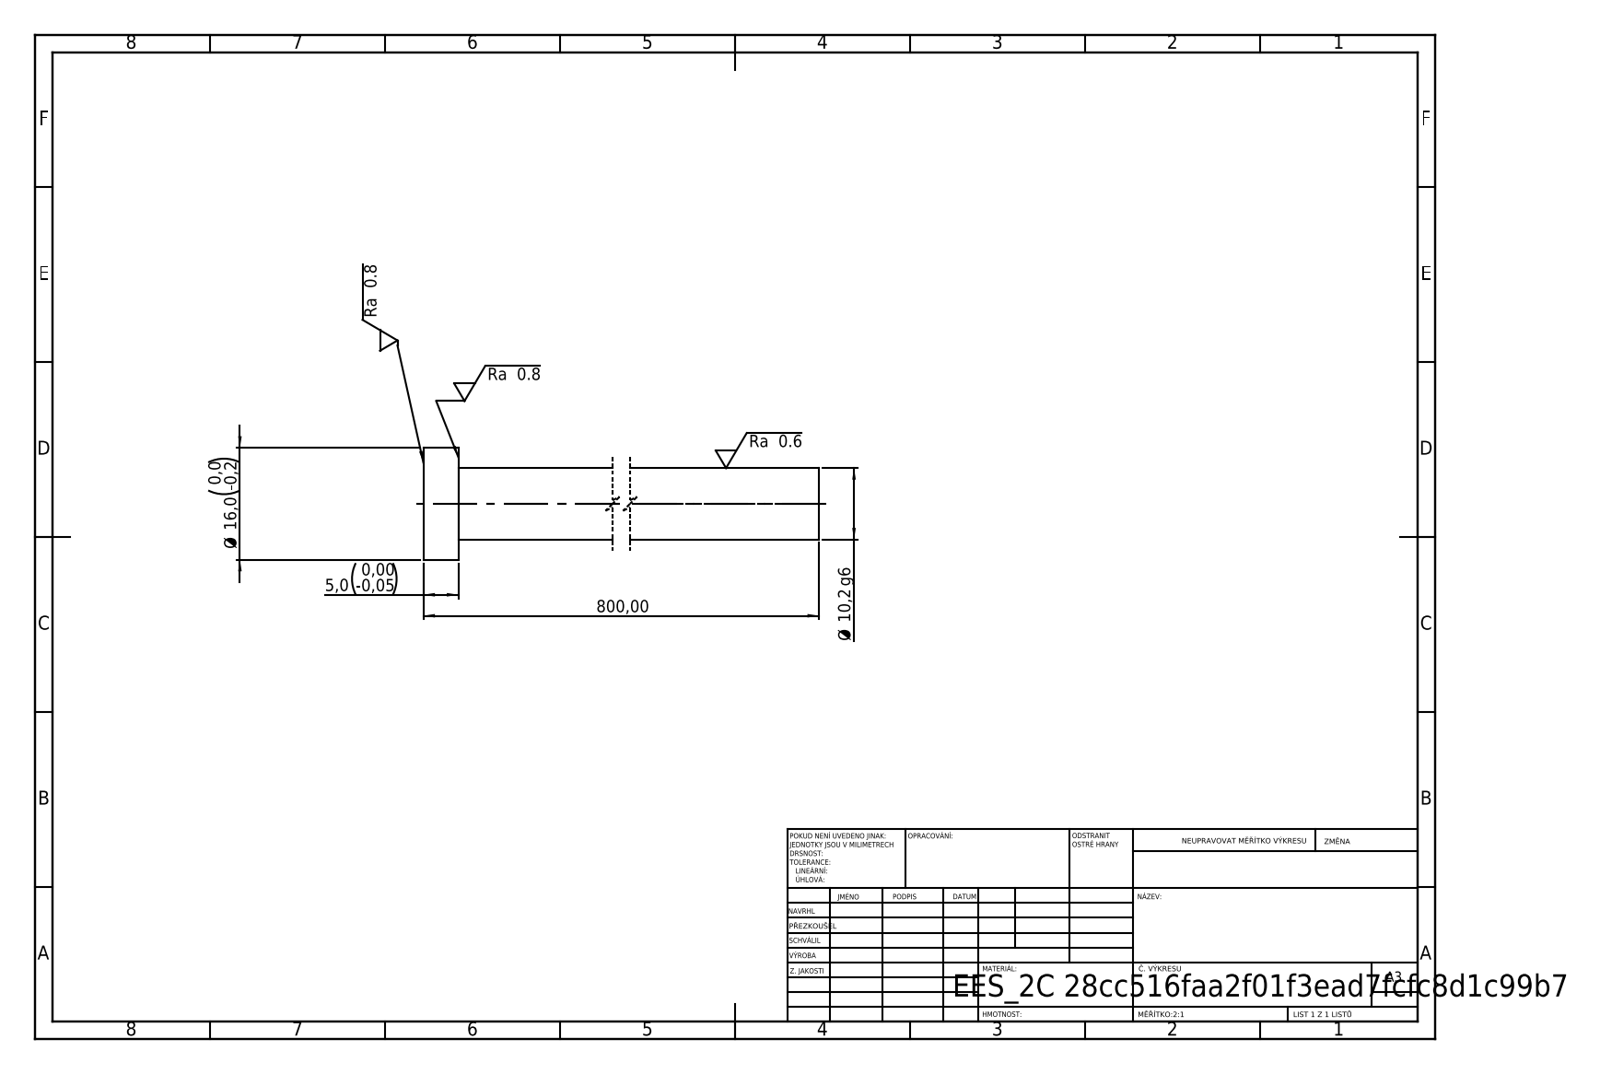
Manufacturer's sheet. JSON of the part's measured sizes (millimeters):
{"step_written_by": "SolidWorks 2019 (CONFIG_CONTROL_DESIGN)", "units": "millimeters", "bodies": {"solids": 1, "faces": 7, "planar": 3, "cylindrical": 4, "other": 0}, "overall_size": [800, 16, 16], "volume_mm3": 65967, "surface_area_mm2": 26129, "round_bosses_or_shafts": [[16, 1], [10.2, 1]], "face_to_face_distances": [5, 800, 795]}
